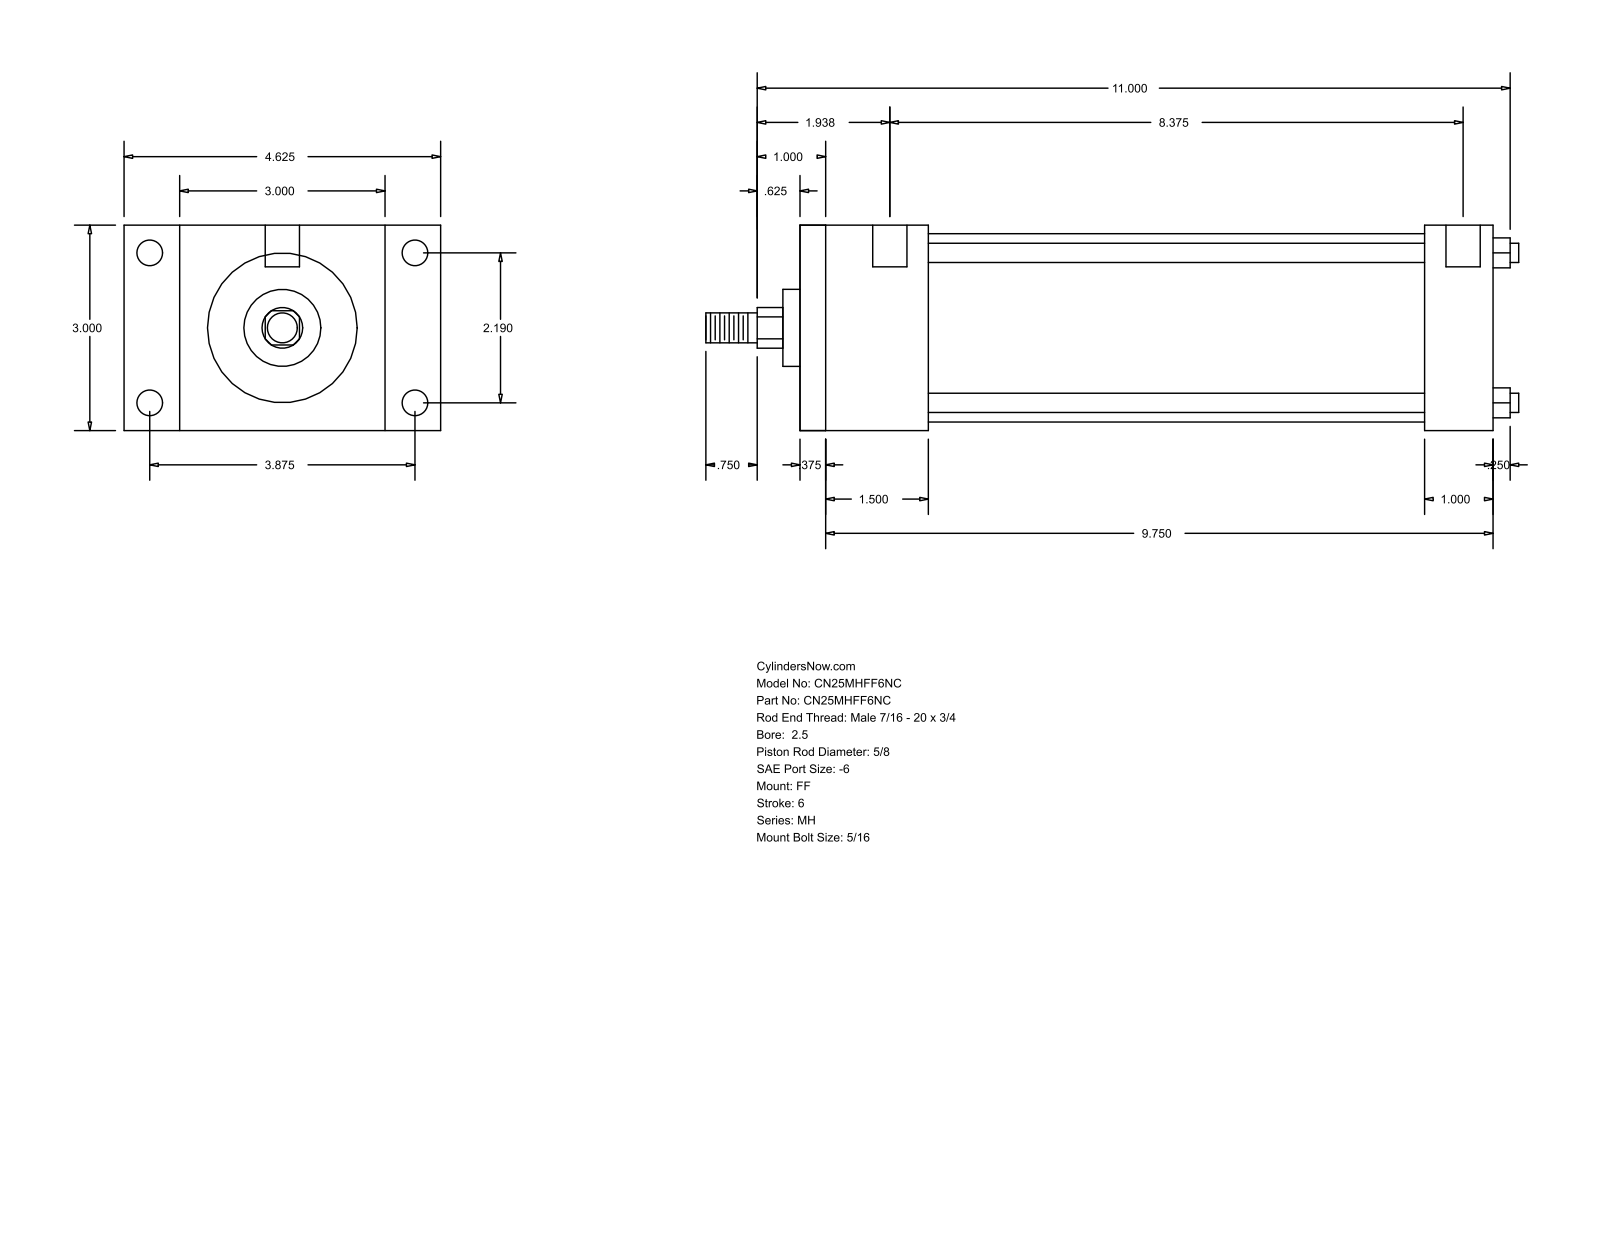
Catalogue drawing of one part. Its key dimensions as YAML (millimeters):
part_name: "MH_FF__0250_0.625"
step_written_by: "GSSL Pune (CONFIG_CONTROL_DESIGN)"
units: millimeters
bodies: {solids: 0, faces: 92, planar: 64, cylindrical: 28, other: 0}
overall_size: [301.62, 117.47, 76.2]
round_holes:
  - {diameter: 5.56, count: 4}
  - {diameter: 9.53, count: 4}
  - {diameter: 12.7, count: 2}
round_bosses_or_shafts:
  - {diameter: 7.14, count: 4}
  - {diameter: 69.85, count: 1}
  - {diameter: 28.57, count: 1}
  - {diameter: 15.88, count: 1}
  - {diameter: 11.11, count: 1}
partial_cylinders:
  - {radius: 7.54, count: 1}
face_to_face_distances: [76.2, 257.17, 9.52, 247.65, 25.4, 47.62, 231.77, 38.1, 222.25, 184.15]
hole_center_spacings: [55.62, 98.42, 113.05, 220.66, 3.17, 4.76, 212.73, 215.9]
